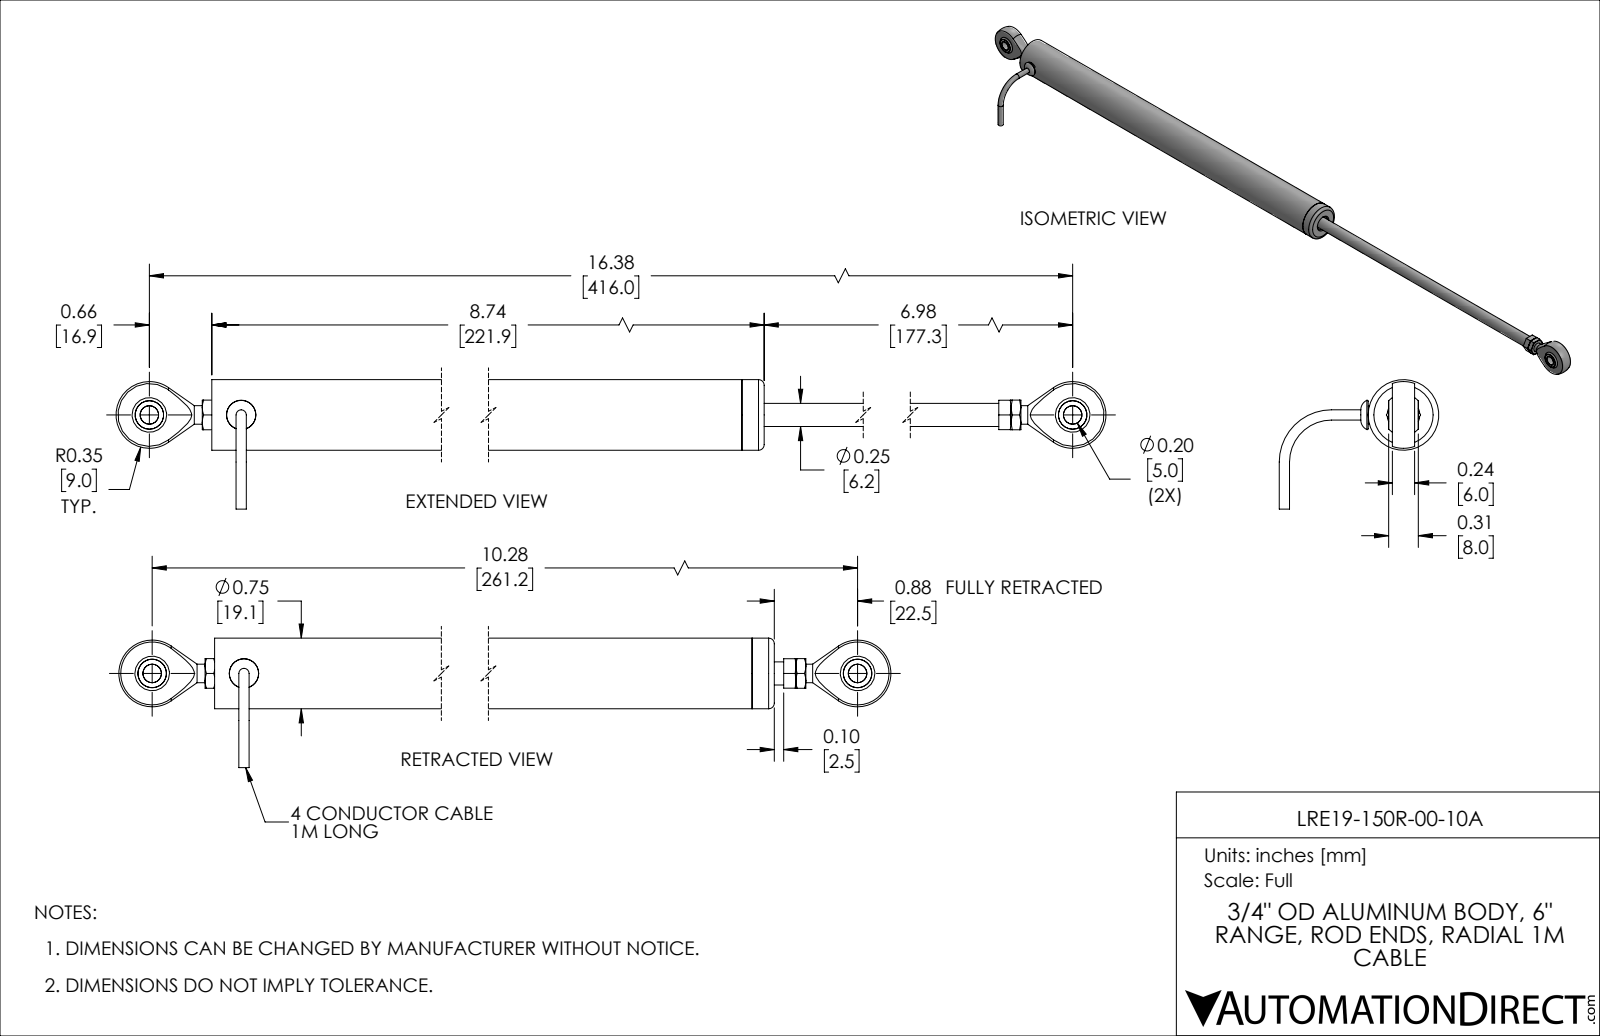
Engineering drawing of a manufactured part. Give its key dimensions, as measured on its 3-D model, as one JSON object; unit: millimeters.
{"part_name": "LRE19-150R-00-10A", "step_written_by": "SolidWorks 2019 (AUTOMOTIVE_DESIGN)", "units": "millimeters", "bodies": {"solids": 13, "faces": 163, "planar": 58, "cylindrical": 34, "other": 71}, "overall_size": [278.2, 43.1, 34.9], "volume_mm3": 27510, "surface_area_mm2": 38410, "round_holes": [[5, 3], [2.8, 1], [4.2, 1], [4.8, 1], [4.9, 1], [5.6, 1], [7.8, 1], [15.7, 1], [15.9, 1], [16.5, 1], [18, 1], [18.4, 1]], "round_bosses_or_shafts": [[19.1, 1], [17.8, 1], [15.8, 1], [6.2, 1], [5.7, 1], [5.5, 1], [2.8, 1]], "face_to_face_distances": [6, 2.7, 219.1, 221.8, 215.8, 213.1, 6, 8, 1, 7], "hole_center_spacings": [24.8, 236.4, 261.2]}
